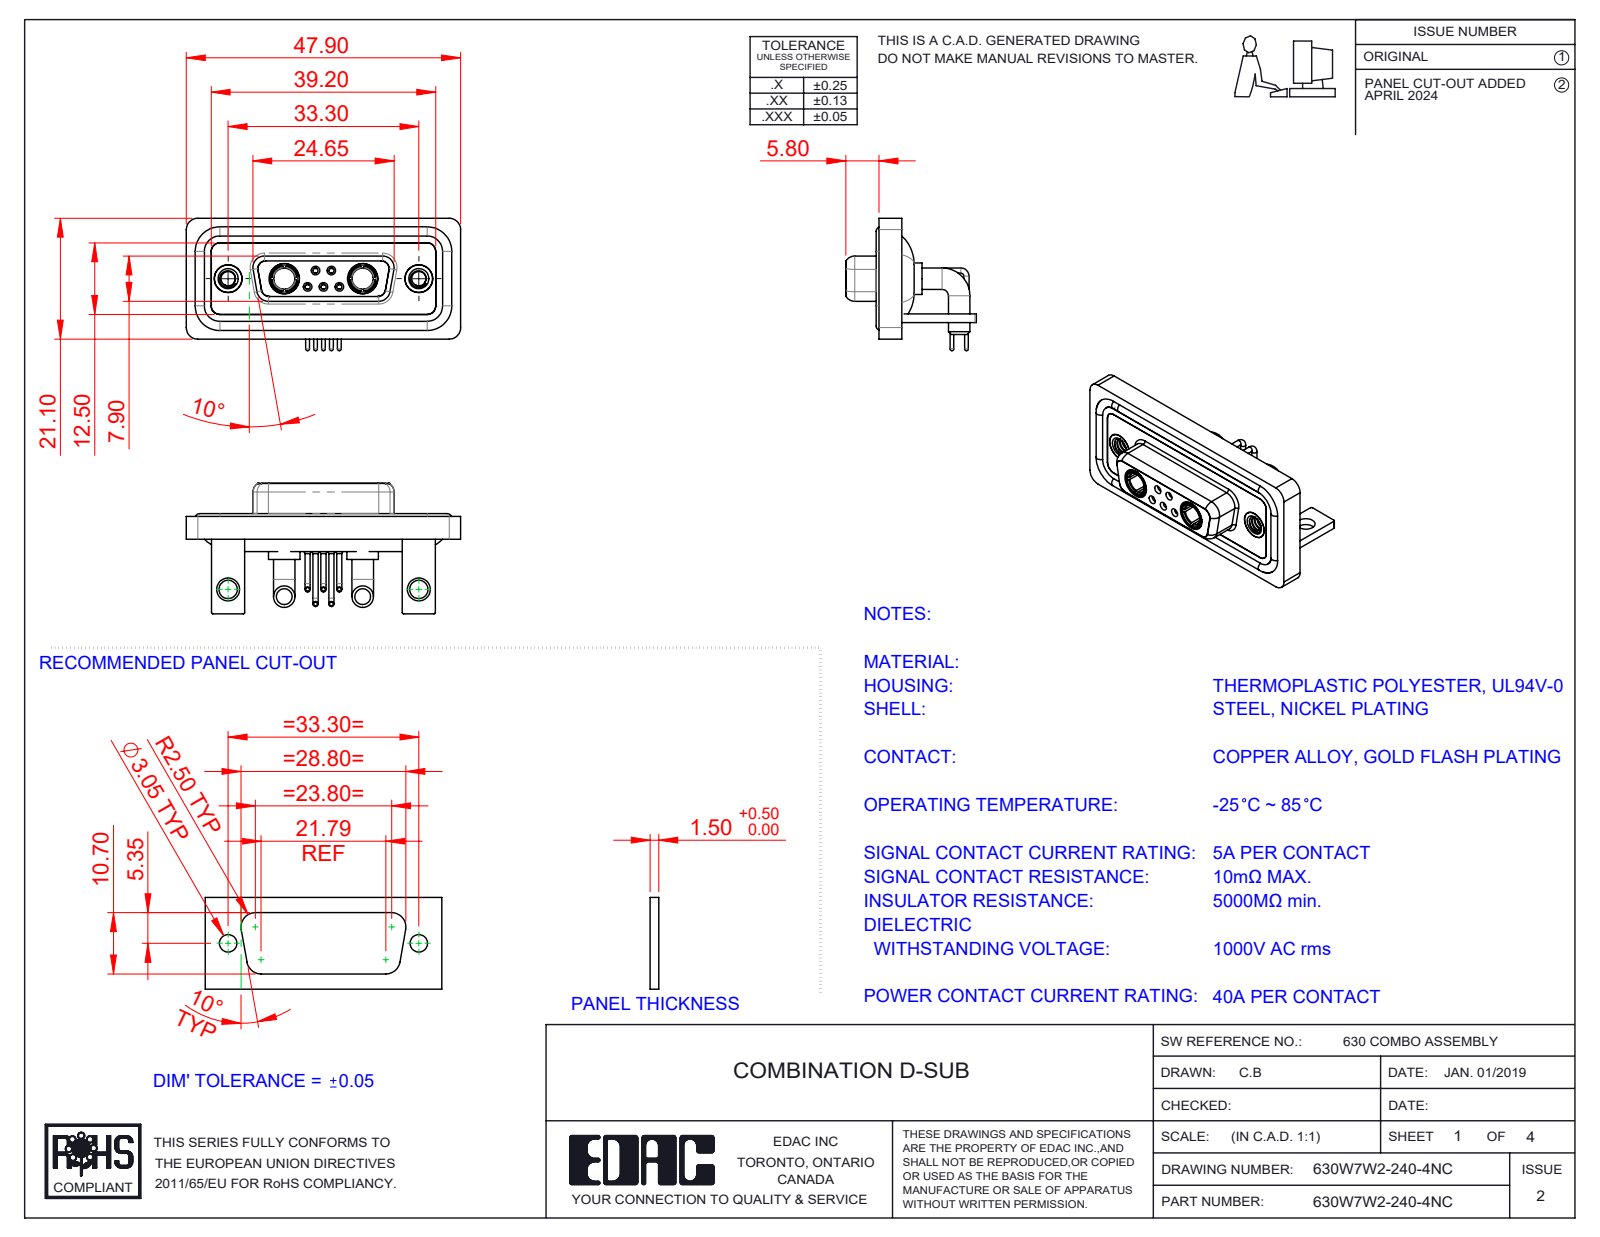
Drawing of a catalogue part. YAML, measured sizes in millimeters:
part_name: "630Combo Stabilizer Bracket_50 Contacts; 630Combo Contact Row 2_50 Contacts; 630Combo Shell Rear_15 Contacts; Power Socket_40A RA (+6 more)"
step_written_by: "SolidWorks 2023 (CONFIG_CONTROL_DESIGN)"
units: millimeters
bodies: {solids: 18, faces: 849, planar: 258, cylindrical: 375, other: 216}
overall_size: [47.9, 23.12, 22.8]
volume: 6701
surface_area: 11032
round_holes:
  - {diameter: 0.9, count: 5}
  - {diameter: 1.1, count: 5}
  - {diameter: 1.5, count: 5}
  - {diameter: 2, count: 5}
  - {diameter: 4.85, count: 4}
  - {diameter: 1.6, count: 3}
  - {diameter: 1.7, count: 2}
  - {diameter: 2.5, count: 2}
  - {diameter: 3.2, count: 2}
  - {diameter: 3.7, count: 2}
  - {diameter: 4, count: 2}
  - {diameter: 4.05, count: 2}
round_bosses_or_shafts:
  - {diameter: 1.6, count: 6}
  - {diameter: 0.9, count: 5}
  - {diameter: 0.65, count: 5}
  - {diameter: 3.75, count: 4}
  - {diameter: 5.5, count: 2}
  - {diameter: 5.2, count: 2}
  - {diameter: 4.96, count: 2}
  - {diameter: 4.95, count: 2}
partial_cylinders:
  - {radius: 2, count: 21}
  - {radius: 1.5, count: 18}
  - {radius: 0.25, count: 16}
  - {radius: 1.35, count: 12}
  - {radius: 1.6, count: 8}
  - {radius: 0.5, count: 5}
  - {radius: 0.6, count: 4}
  - {radius: 0.65, count: 4}
face_to_face_distances: [0.4, 2.9, 1.5, 1.8, 3.7, 1.1, 4.1, 1.6, 2.5, 1.4]
hole_center_spacings: [3.16, 2.77, 9.8, 23.5, 33.3, 4.31, 4.33, 5.03]
